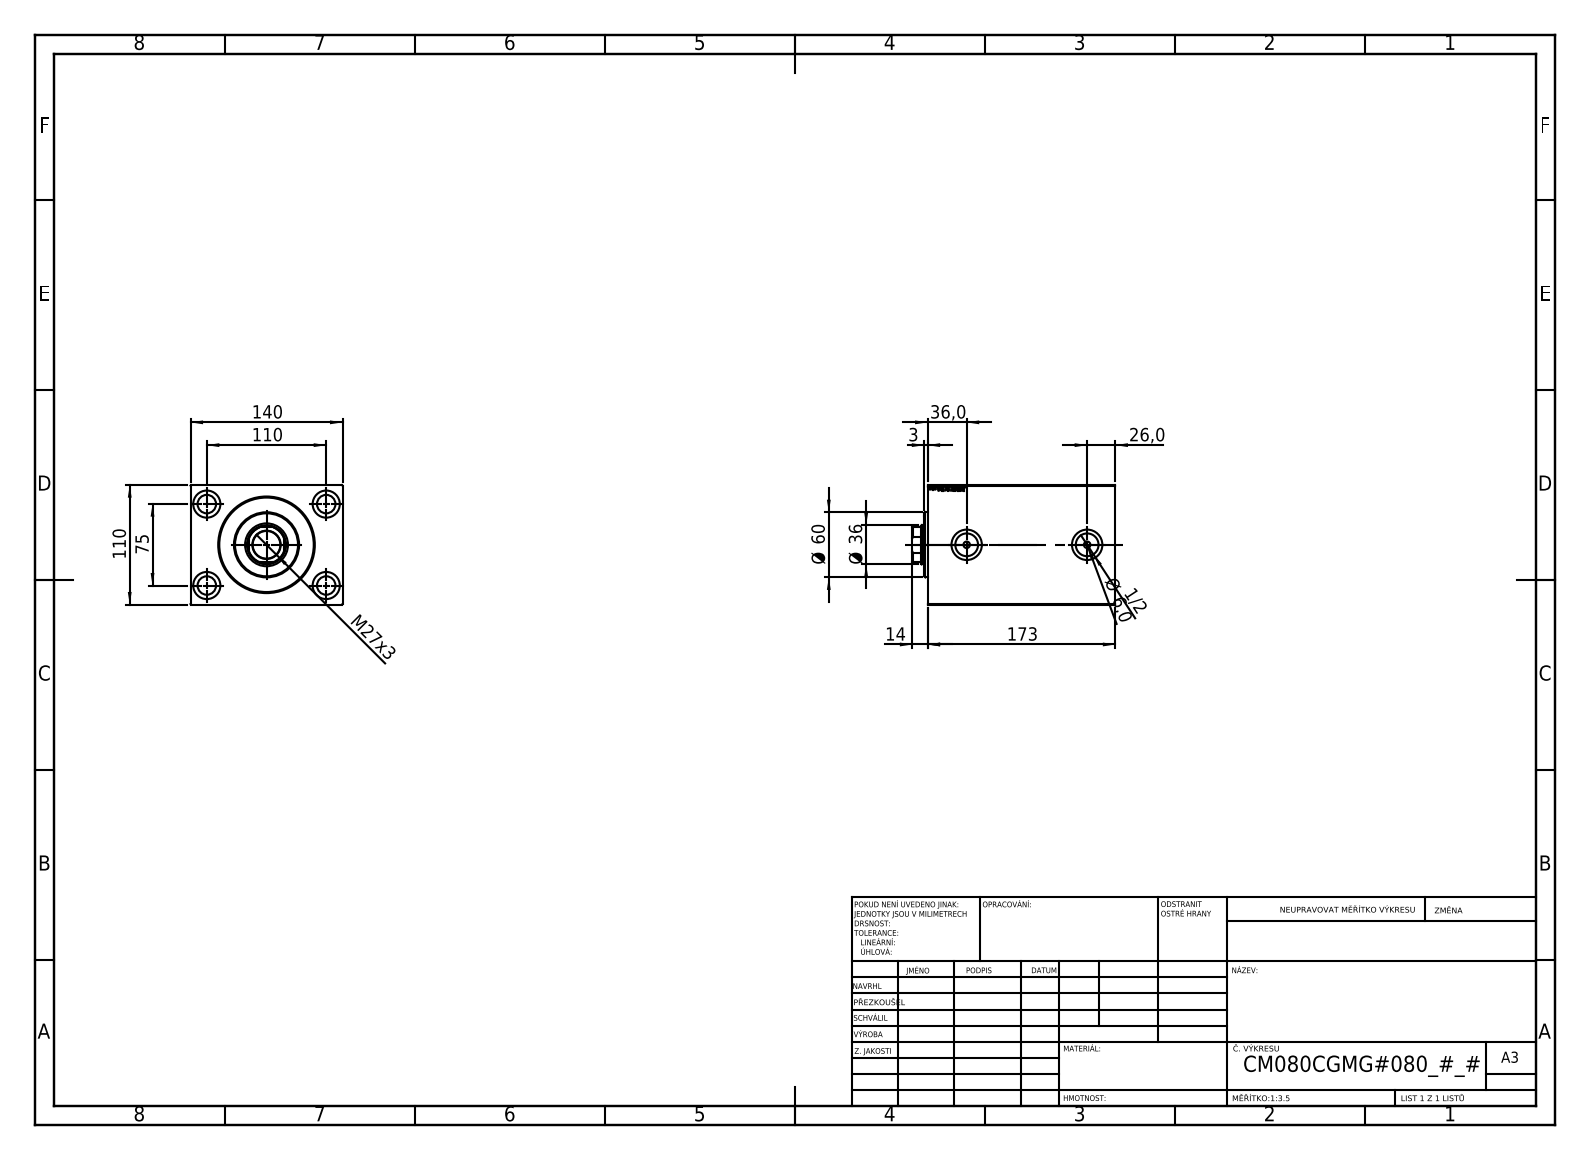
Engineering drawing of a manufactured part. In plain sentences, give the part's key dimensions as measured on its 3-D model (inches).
The part is named "V450CM_C_VCP; V450CM_VC_B; V450CM_C_Body". Its 3-D file was written by "SolidWorks 2019 (CONFIG_CONTROL_DESIGN)". It is 3 solids with 865 faces: 409 planar, 62 cylindrical and 394 other. Overall it measures 7.362 by 5.512 by 4.331 inches. Its volume is 130.7 cubic inches and its surface area 390 square inches. Round holes: 4 of diameter 0.669, 4 of diameter 0.984, 2 of diameter 0.236, 2 of diameter 0.825, 2 of diameter 1.102, 1 of diameter 1.004, 1 of diameter 1.417, 1 of diameter 1.555, 1 of diameter 3.15, 1 of diameter 3.228, 1 of diameter 3.425. Round bosses or shafts: 1 of diameter 2.362. Partial cylindrical surfaces (rounded edges, fillets, slot ends): 1 of radius 0.689. The main face-to-face distances are 4.331, 5.512, 6.811, 5.984, 0.827, 6.26, 0.551, 5.433, 3.701, 3.15. The hole center spacings are 2.621, 2.953, 4.331, 5.242, 4.37.
